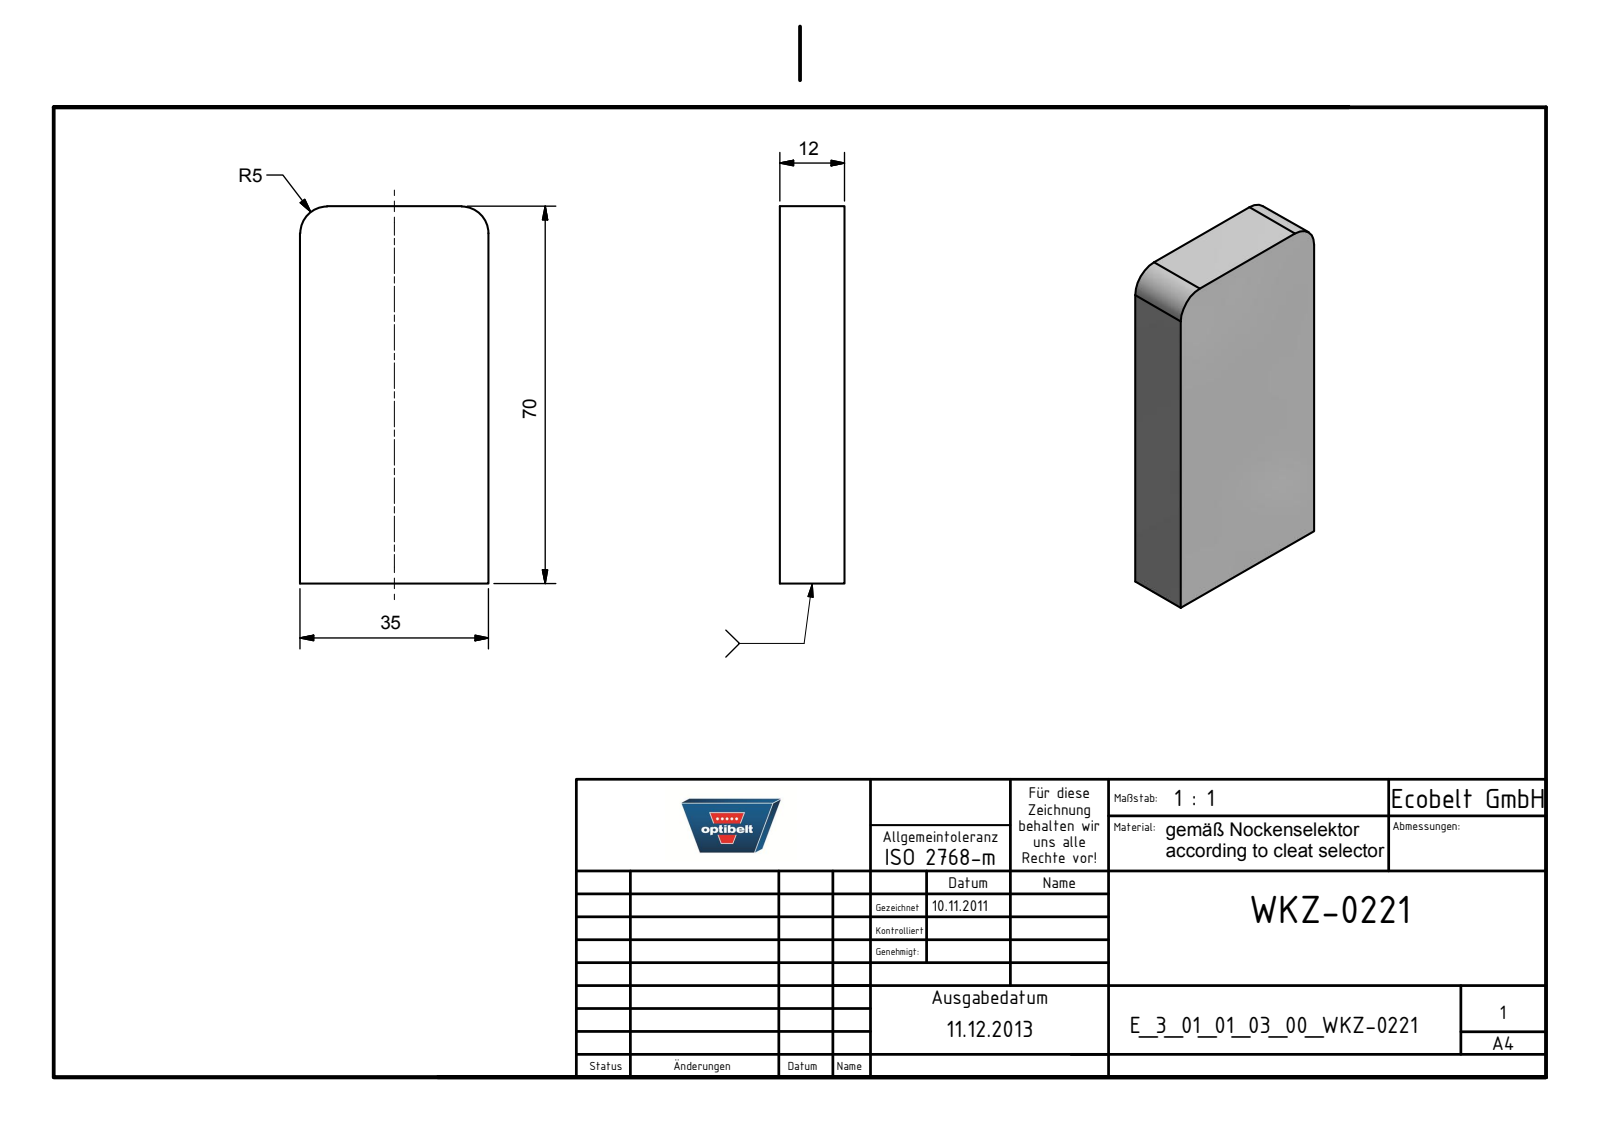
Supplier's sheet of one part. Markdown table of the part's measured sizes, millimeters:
| quantity | value |
| --- | --- |
| part name | E_3_01_01_03_00_WKZ-0221 |
| STEP written by | Autodesk Inventor 2021 (AUTOMOTIVE_DESIGN) |
| units | millimeters |
| bodies | 1 solid, 8 faces (6 planar, 2 cylindrical, 0 other) |
| overall size | 70 × 35 × 12 |
| volume | 29 271 mm³ |
| surface area | 7 347 mm² |
| partial cylindrical surfaces (radius × count) | 5 × 2 |
| main face-to-face distances | 12, 35, 70 |
